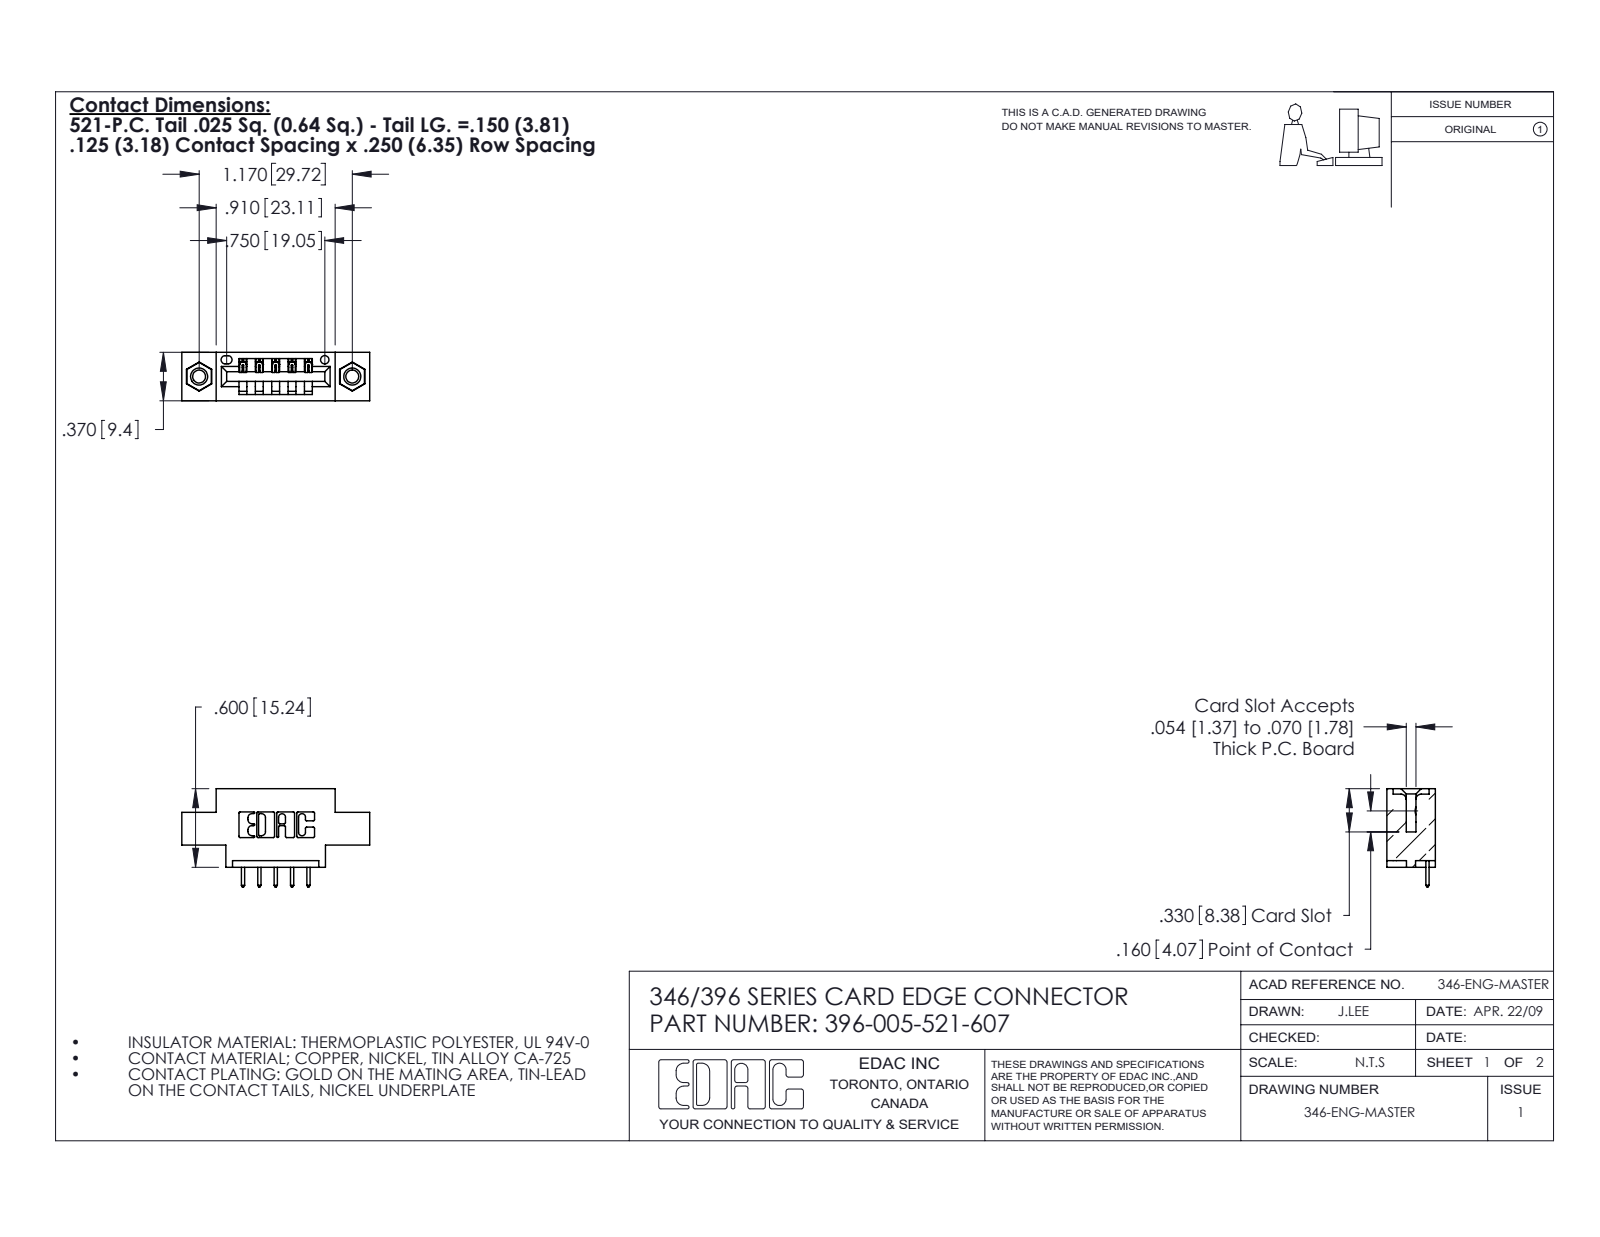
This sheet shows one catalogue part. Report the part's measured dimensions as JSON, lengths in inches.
{"part_name": "345-292-001_345-293-121; 345-250-001_345-250-005-103; 346 Part_0.170 Offset - 0.156 Dia-TI; 396-005-521-607", "step_written_by": "SolidWorks 2020 (CONFIG_CONTROL_DESIGN)", "units": "inches", "bodies": {"solids": 8, "faces": 476, "planar": 312, "cylindrical": 148, "other": 16}, "overall_size": [1.435, 0.75, 0.37], "volume_in3": 0.186, "surface_area_in2": 5.508, "round_holes": [[0.098, 2], [0.125, 2], [0.156, 2], [0.064, 1]], "round_bosses_or_shafts": [[0.155, 2]], "partial_cylinders_radius": [[0.01, 22], [0.006, 10], [0.01, 10], [0.007, 6], [0.031, 6], [0.026, 3], [0.031, 2], [0.04, 2]], "face_to_face_distances": [0.25, 0.37, 0.048, 0.322, 0.222, 0.148, 0.1, 0.174, 0.55, 0.125], "hole_center_spacings": [0.246, 0.969, 1.17]}
